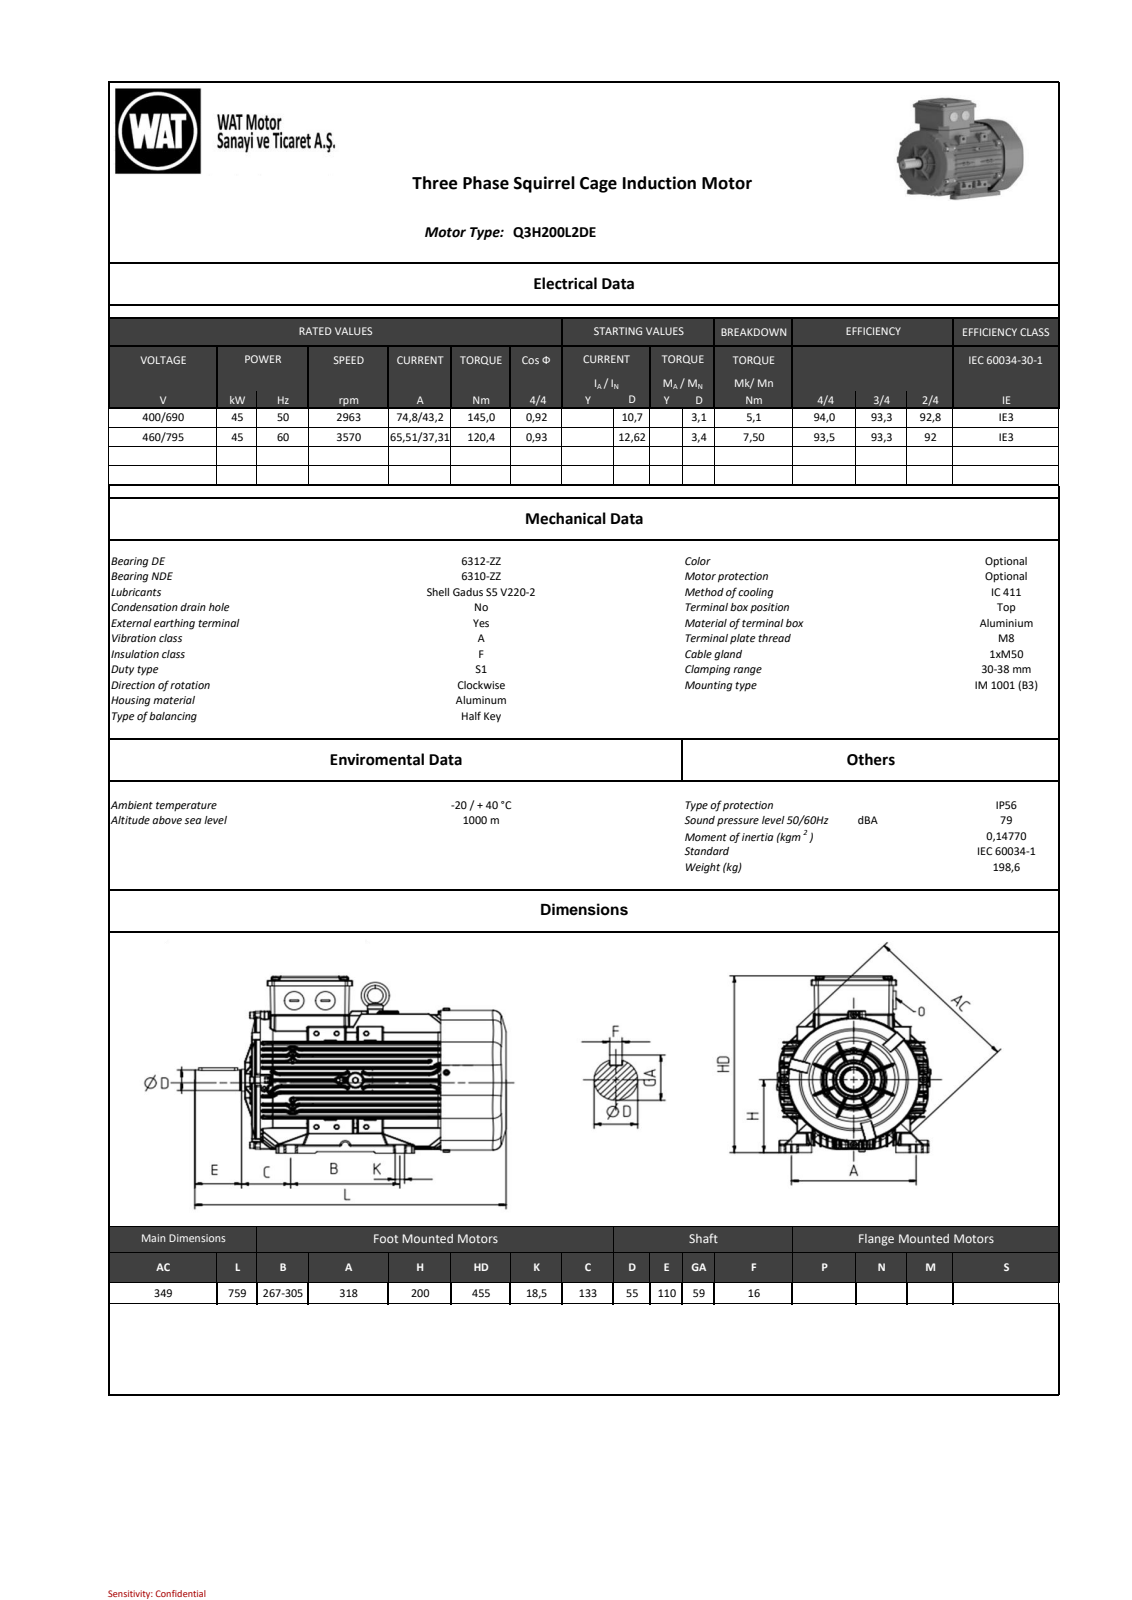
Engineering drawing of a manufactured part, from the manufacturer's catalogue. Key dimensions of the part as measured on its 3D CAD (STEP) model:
Part name (STEP PRODUCT): model1_objects
STEP written by: SIEMENS PLM Software NX2206.8101 (AUTOMOTIVE_DESIGN)
Units: millimetres
Bodies: 0 solids, 15515 faces (4112 planar, 5962 cylindrical, 5441 other)
Overall size (bounding box): 759 × 452 × 387.89
Round holes (diameter × count): ⌀5.6 ×8, ⌀0.4 ×4, ⌀4.3 ×4, ⌀5.5 ×4, ⌀6.5 ×4, ⌀8.3 ×4, ⌀10.45 ×4, ⌀4 ×3, ⌀9.44 ×2, ⌀25.05 ×2, ⌀44 ×2, ⌀7.6 ×1
Round bosses / shafts (diameter × count): ⌀10 ×6, ⌀18.1 ×4, ⌀16 ×4, ⌀14.8 ×4, ⌀13 ×4, ⌀12 ×4, ⌀9.5 ×4, ⌀8 ×4
Partial cylindrical surfaces — rounded edges, fillets, slot ends (radius × count): R0.5 ×1684, R2 ×1176, R1 ×1052, R3 ×328, R0.1 ×122, R4 ×102, R5 ×61, R8 ×33
Main face-to-face distances: 1.2, 6, 16.21, 32.48, 16.27, 171.05, 173.83, 141.35, 157.62, 154.78
Hole centre spacings: 136, 78.16, 169.96, 156, 161, 227.69, 68.17, 68.2
